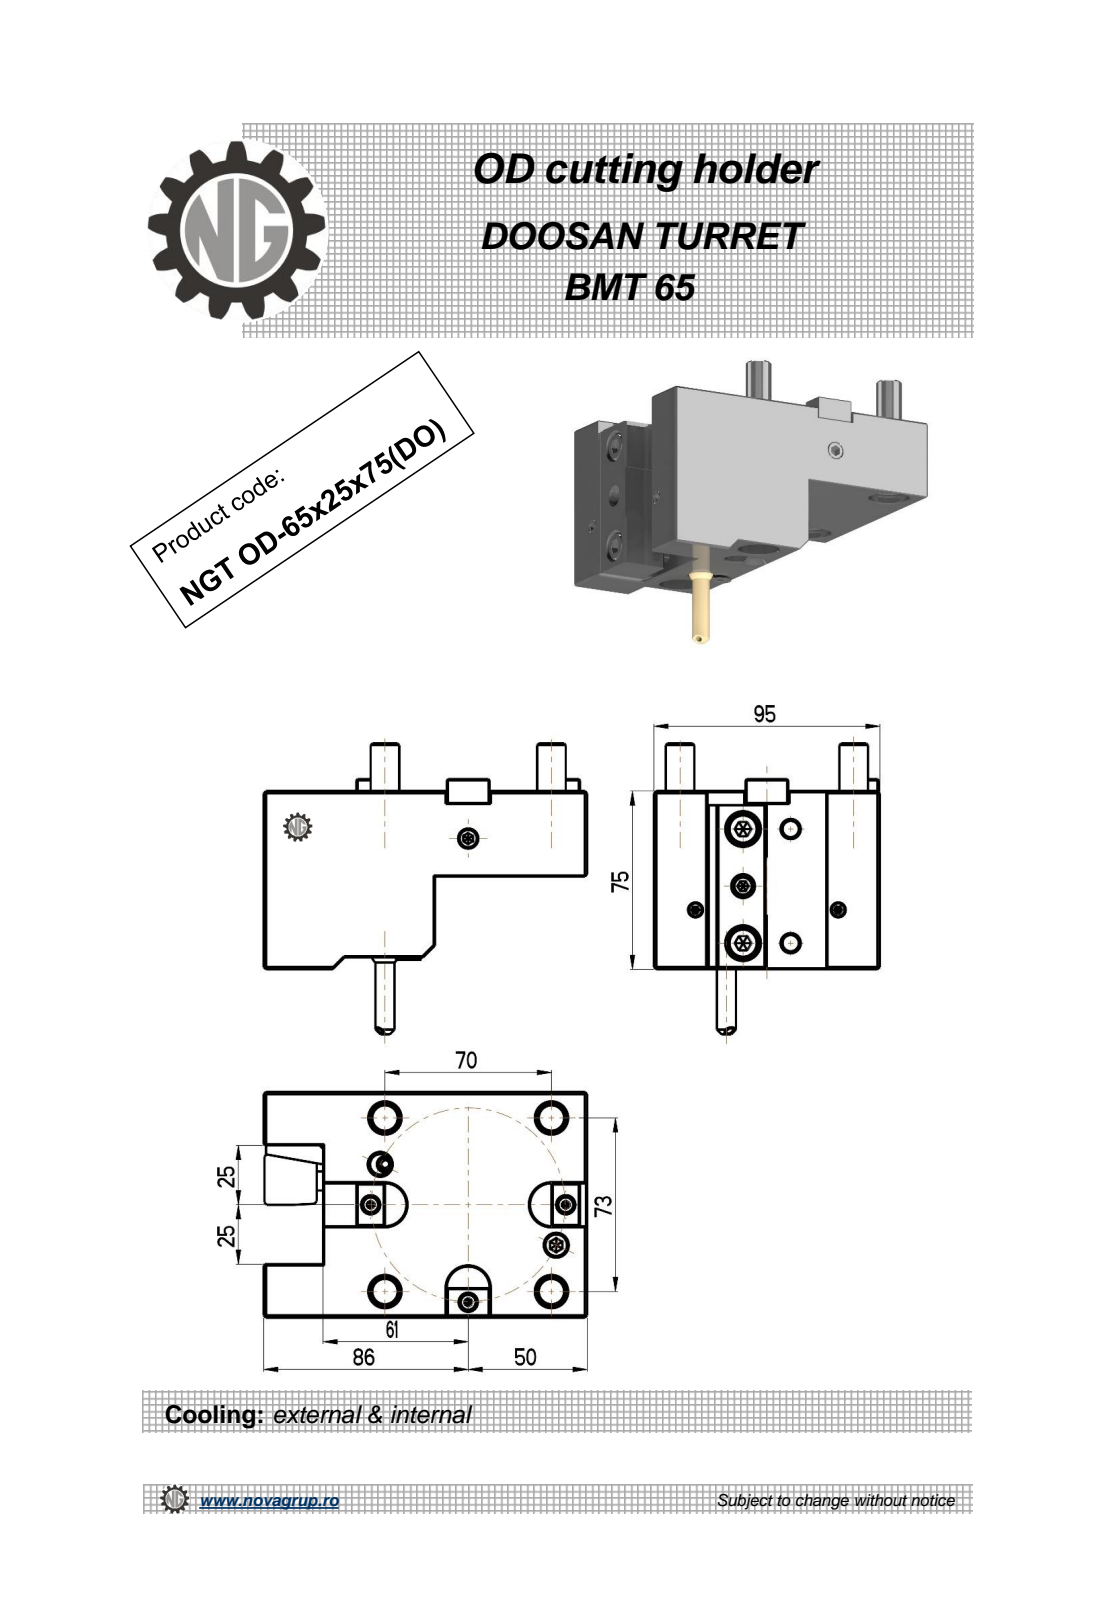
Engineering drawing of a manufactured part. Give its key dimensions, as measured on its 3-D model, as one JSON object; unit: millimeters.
{"part_name": "NGT_OD_65_25_75_DO", "step_written_by": "PRO/ENGINEER BY PARAMETRIC TECHNOLOGY CORPORATION, 2010280 (CONFIG_CONTROL_DESIGN)", "units": "millimeters", "bodies": {"solids": 1, "faces": 233, "planar": 161, "cylindrical": 38, "other": 34}, "overall_size": [136, 122.34, 95], "volume_mm3": 664224, "surface_area_mm2": 65667, "round_holes": [[3, 1], [5, 1], [8.5, 1]], "round_bosses_or_shafts": [[12, 4], [8, 4], [11.2, 1]], "partial_cylinders_radius": [[0.22, 6], [0.51, 6], [9, 3]], "face_to_face_distances": [95, 36, 25, 70, 47, 34, 64, 111, 136, 72], "hole_center_spacings": [2]}
